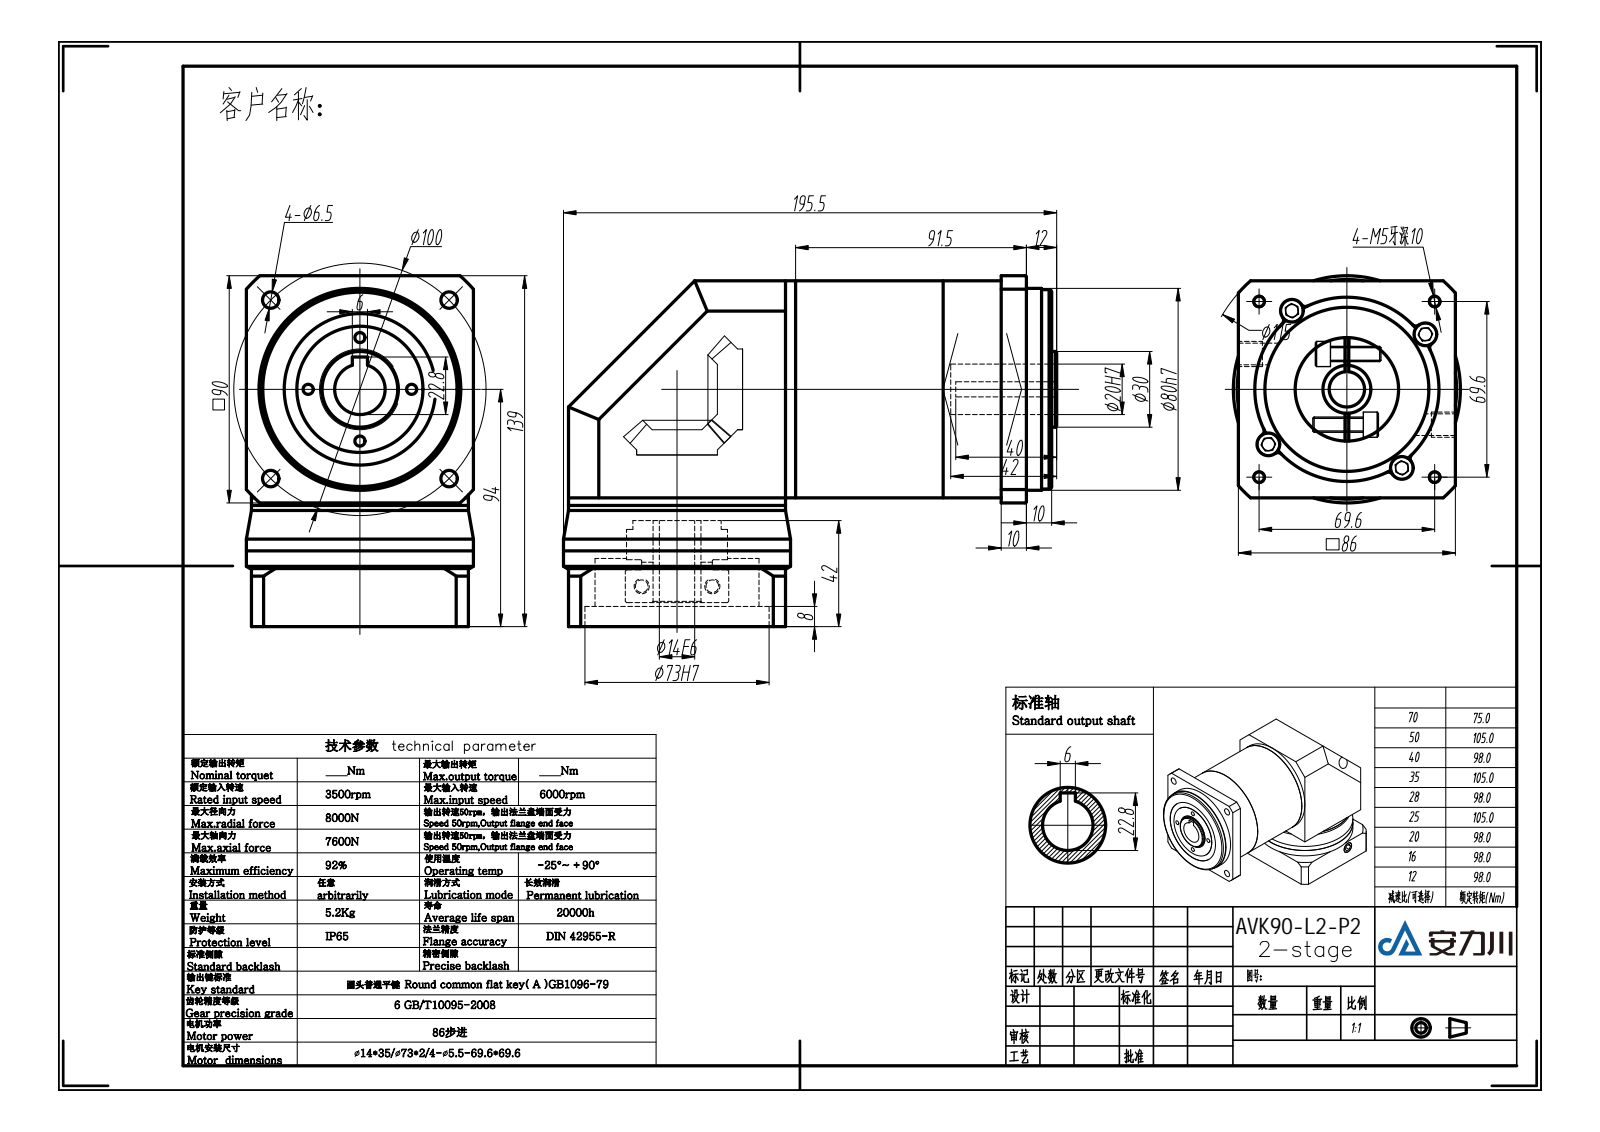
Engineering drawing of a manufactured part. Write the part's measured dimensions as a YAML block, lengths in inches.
part_name: "VGZK85双级模型（14-35 73-2 4-5.5-69.6-69.6）新"
step_written_by: "SolidWorks 2016 (AUTOMOTIVE_DESIGN)"
units: inches
bodies: {solids: 6, faces: 359, planar: 195, cylindrical: 144, other: 20}
overall_size: [7.697, 5.472, 3.543]
volume: 82.63
surface_area: 259.5
round_holes:
  - {diameter: 0.394, count: 8}
  - {diameter: 0.157, count: 4}
  - {diameter: 0.165, count: 4}
  - {diameter: 0.256, count: 4}
  - {diameter: 0.354, count: 4}
  - {diameter: 0.787, count: 2}
  - {diameter: 0.551, count: 1}
  - {diameter: 0.748, count: 1}
  - {diameter: 1.268, count: 1}
  - {diameter: 2.362, count: 1}
  - {diameter: 2.559, count: 1}
round_bosses_or_shafts:
  - {diameter: 0.335, count: 6}
  - {diameter: 0.331, count: 4}
  - {diameter: 3.386, count: 2}
  - {diameter: 0.386, count: 2}
  - {diameter: 3.543, count: 1}
  - {diameter: 3.15, count: 1}
  - {diameter: 3.11, count: 1}
  - {diameter: 1.969, count: 1}
partial_cylinders:
  - {radius: 0.079, count: 8}
  - {radius: 1.437, count: 1}
  - {radius: 2.264, count: 1}
  - {radius: 2.362, count: 1}
face_to_face_distances: [0.709, 2.303, 3.386, 3.543, 0.394, 0.157, 0.118, 0.827, 5.846, 1.693]
hole_center_spacings: [1.496, 1.51, 2.603, 0.811, 0.82, 1.402, 1.953, 1.965]
